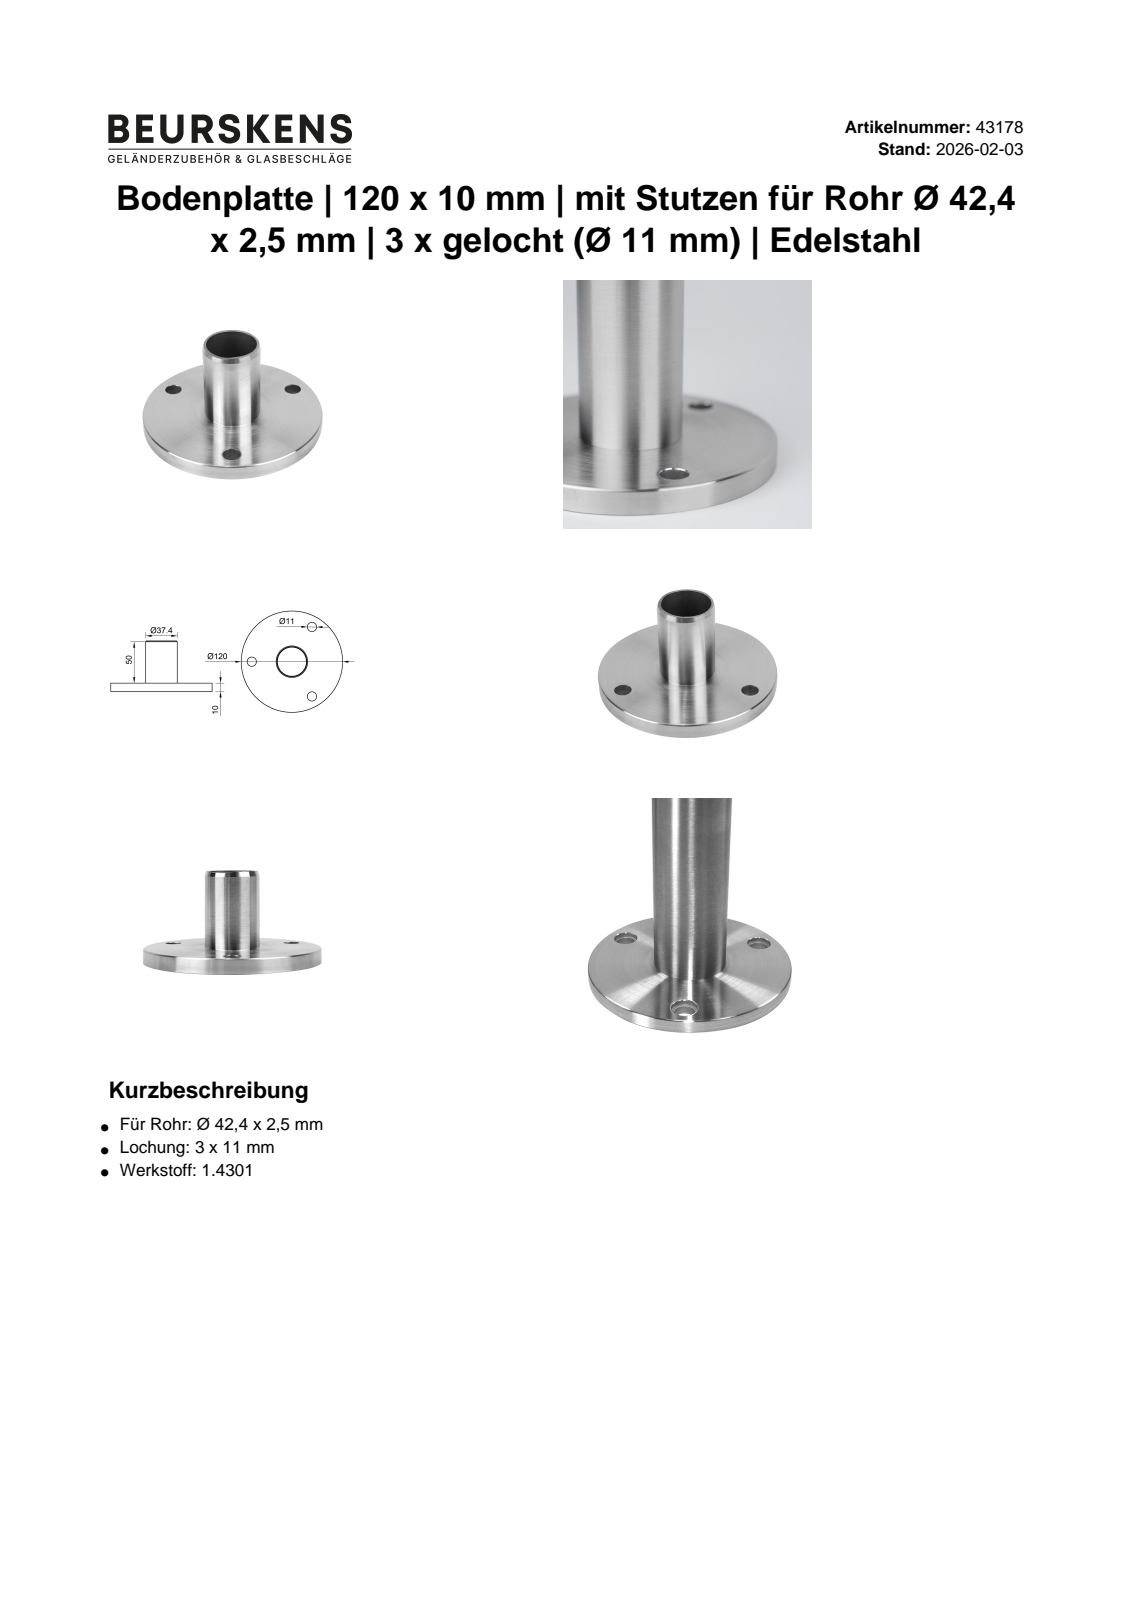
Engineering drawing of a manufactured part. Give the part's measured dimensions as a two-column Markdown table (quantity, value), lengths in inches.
| quantity | value |
| --- | --- |
| part name | 43178 |
| STEP written by | Autodesk Inventor 2022 (AUTOMOTIVE_DESIGN) |
| units | inches |
| bodies | 1 solid, 10 faces (3 planar, 6 cylindrical, 1 other) |
| overall size | 4.724 × 4.724 × 2.362 |
| volume | 6.673 in³ |
| surface area | 57.79 in² |
| round holes (diameter × count) | 0.433 × 3, 1.354 × 1 |
| round bosses / shafts (diameter × count) | 4.724 × 1, 1.472 × 1 |
| main face-to-face distances | 0.394, 2.362, 1.969 |
| hole center spacings | 1.87, 3.239, 3.239 |
